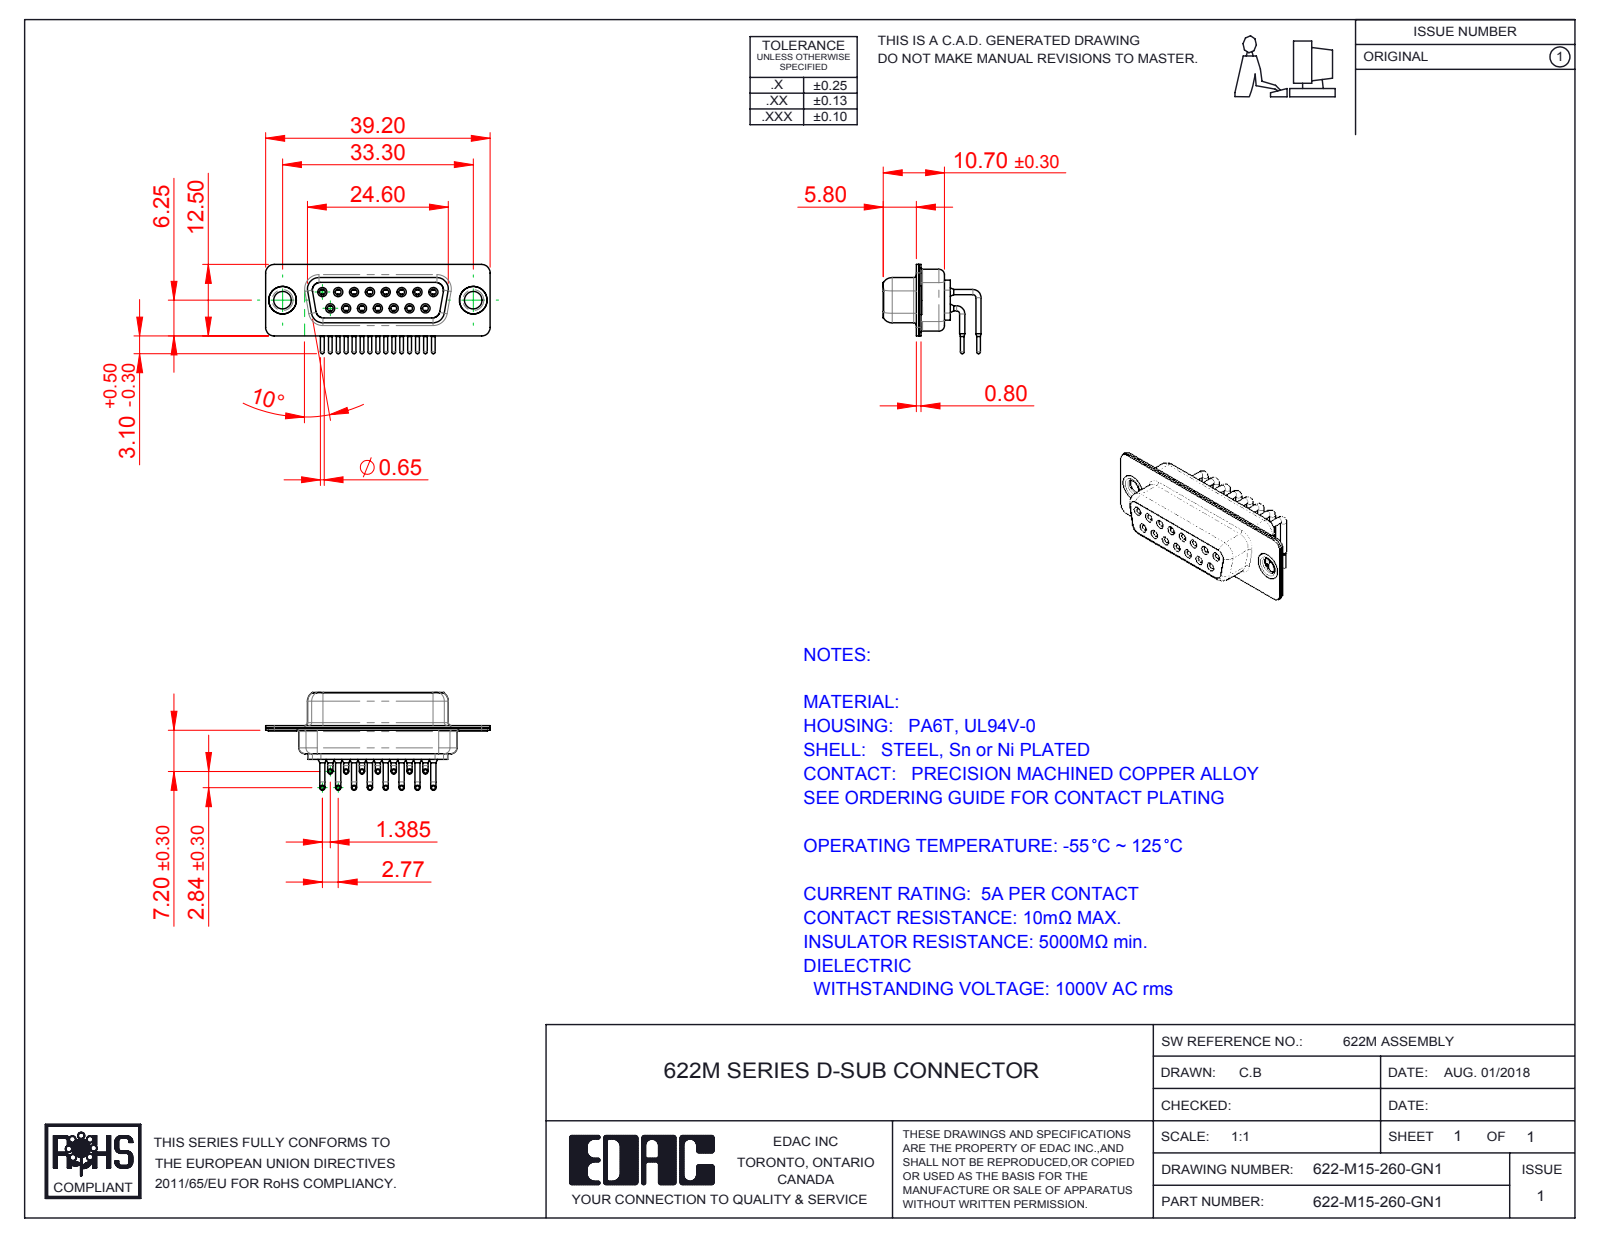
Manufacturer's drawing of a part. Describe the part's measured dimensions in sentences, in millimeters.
The part is named "622-M15-260-GN1; 622M Thru Hole Rivet; 622M Contact Row 2; 622M Contact Row 1 (+3 more)". Its 3-D file was written by "SolidWorks 2016 (CONFIG_CONTROL_DESIGN)". It is 20 solids with 1048 faces: 292 planar, 466 cylindrical and 290 other. Overall it measures 39.2 by 17.09 by 15.6 millimeters. Its volume is 2 461 cubic millimeters and its surface area 6 268 square millimeters. Round holes: 15 of diameter 1, 15 of diameter 1.1, 15 of diameter 1.7, 15 of diameter 1.8, 15 of diameter 2, 2 of diameter 3.05, 2 of diameter 4, 2 of diameter 4.8. Round bosses or shafts: 30 of diameter 0.9, 15 of diameter 1.6, 15 of diameter 1.5, 15 of diameter 0.65, 2 of diameter 5, 2 of diameter 4.9, 2 of diameter 3.55. Partial cylindrical surfaces (rounded edges, fillets, slot ends): 16 of radius 1.5, 12 of radius 2, 8 of radius 1.35, 8 of radius 1.6, 4 of radius 0.25, 4 of radius 0.5, 4 of radius 0.6, 4 of radius 0.65. The main face-to-face distances are 0.4, 1.45, 8.95, 6.2, 1.9, 8.5, 2.3, 0.45, 7.05, 0.85. The hole center spacings are 3.16, 2.77, 5.54, 8.31, 11.08, 5.03, 5.04, 7.48.
